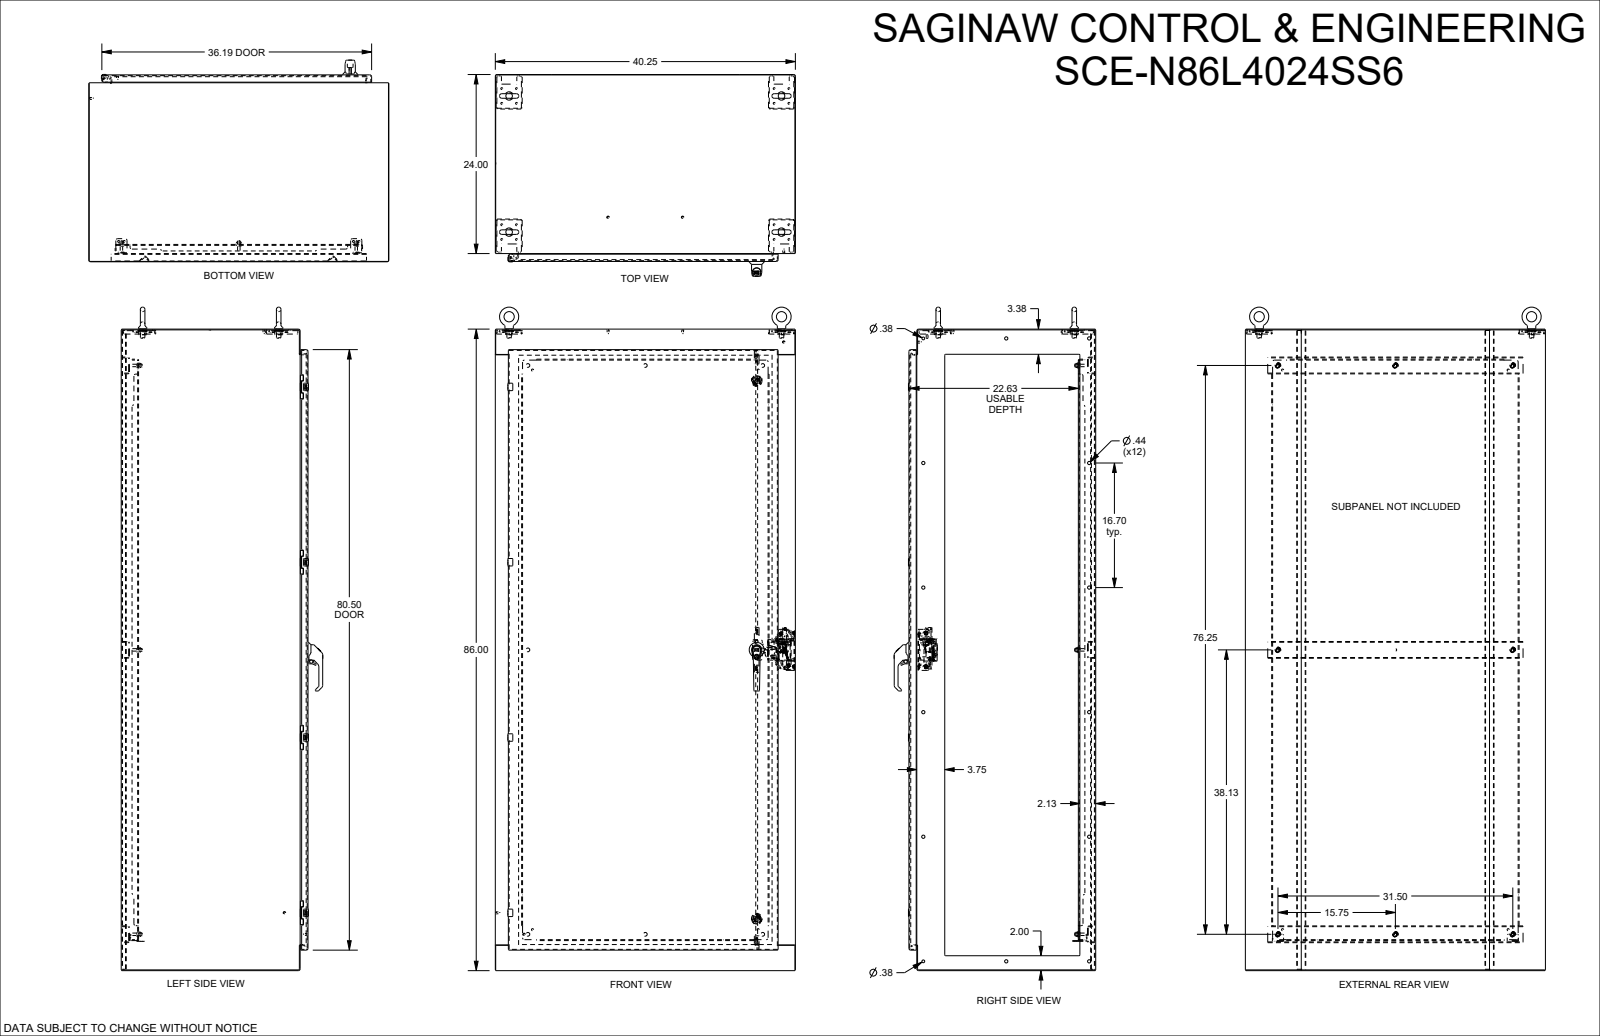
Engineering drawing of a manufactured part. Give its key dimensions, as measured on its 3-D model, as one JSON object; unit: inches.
{"part_name": "SCE-N86L4024", "step_written_by": "SolidWorks 2023 (AUTOMOTIVE_DESIGN)", "units": "inches", "bodies": {"solids": 30, "faces": 4201, "planar": 1646, "cylindrical": 1467, "other": 1088}, "overall_size": [88.945, 40.25, 27.046], "volume_in3": 1364, "surface_area_in2": 25807, "round_holes": [[0.25, 18], [0.437, 12], [0.375, 10], [0.205, 8], [0.244, 8], [0.04, 4], [0.17, 4], [0.218, 4], [0.256, 4], [0.875, 4], [0.135, 2], [0.156, 2]], "round_bosses_or_shafts": [[0.17, 12], [0.25, 11], [0.24, 8], [0.196, 5], [1.173, 4], [0.6, 4], [1.4, 2], [0.48, 2]], "partial_cylinders_radius": [[0.03, 129], [0.015, 108], [0.125, 87], [0.063, 43], [0.02, 38], [0.167, 38], [0.229, 32], [0.25, 27]], "face_to_face_distances": [0.104, 24.954, 25.058, 24.85, 0.104, 85.896, 23.896, 1.058, 40.146, 85.792], "hole_center_spacings": [1.979, 1.4, 23.5, 16.7, 27.82, 2.799, 17.289, 18.25]}
